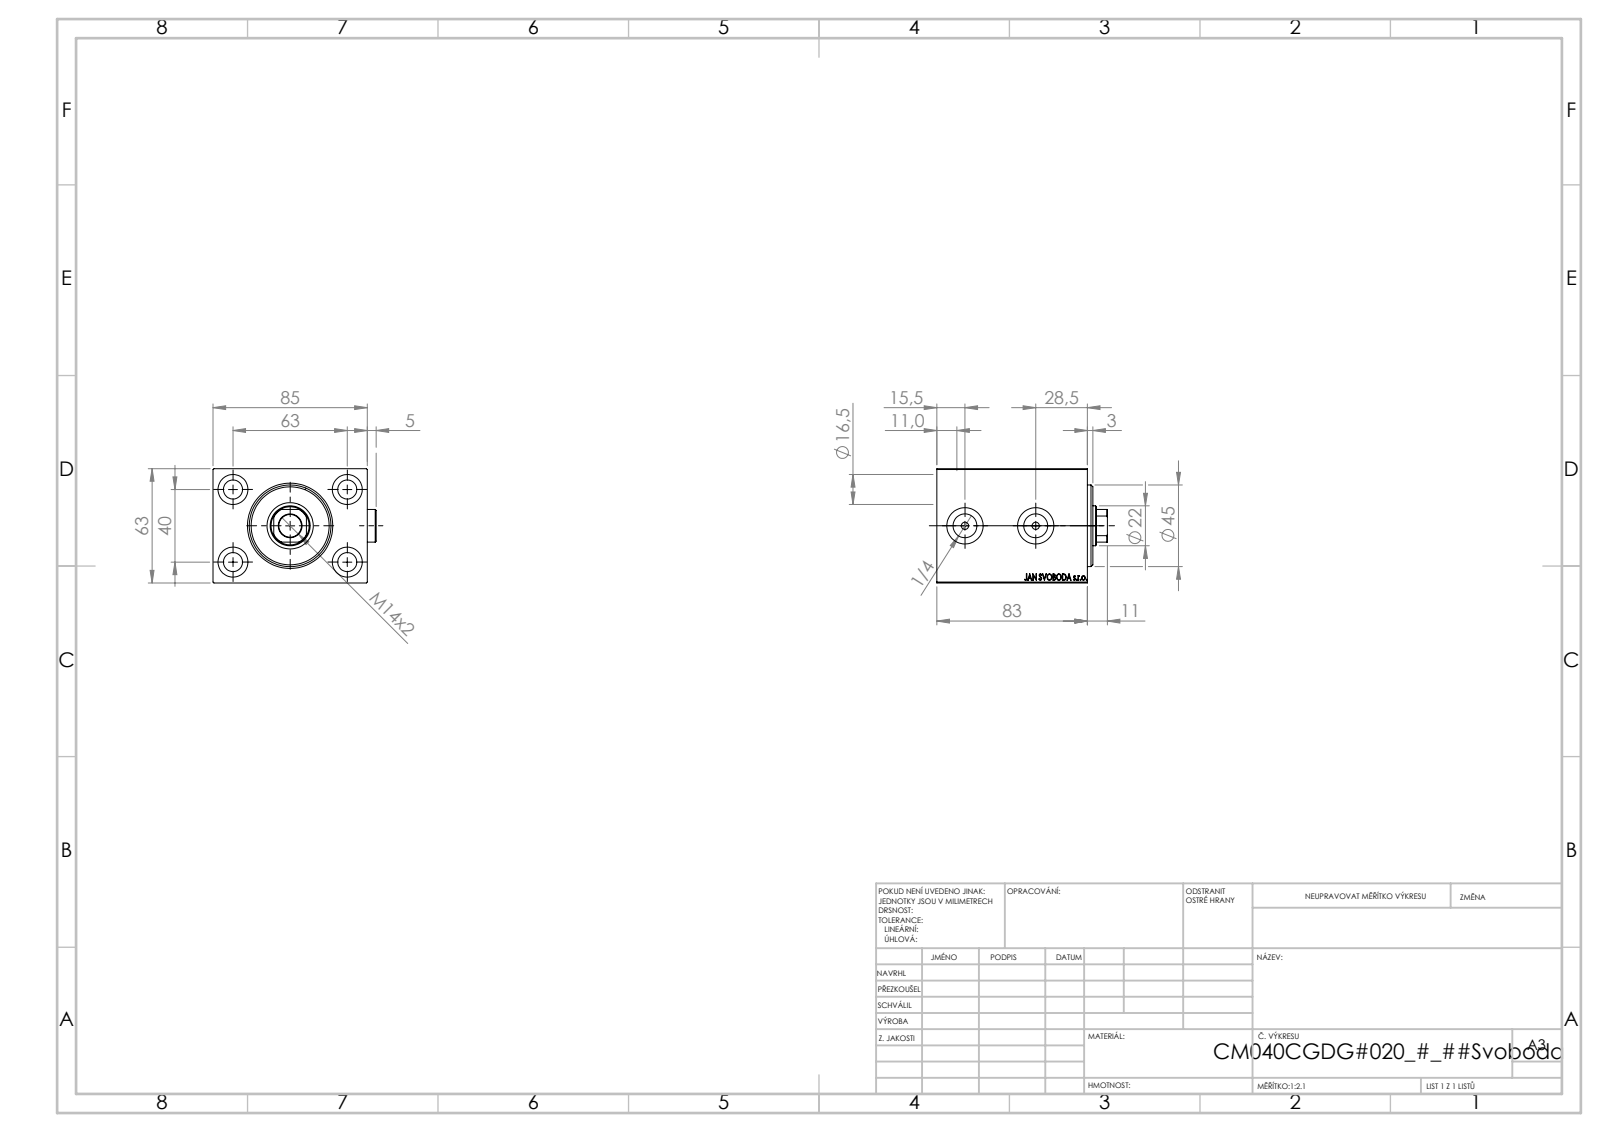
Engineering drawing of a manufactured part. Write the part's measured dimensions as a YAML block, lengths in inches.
part_name: "Zatka_OIL_PORT; V450CM_C_VCP; V450CM_VC_B; V450CM_C_Body"
step_written_by: "SolidWorks 2019 (CONFIG_CONTROL_DESIGN)"
units: inches
bodies: {solids: 5, faces: 914, planar: 442, cylindrical: 74, other: 398}
overall_size: [3.701, 3.539, 2.48]
volume: 24.06
surface_area: 115.4
round_holes:
  - {diameter: 0.413, count: 4}
  - {diameter: 0.65, count: 4}
  - {diameter: 0.157, count: 2}
  - {diameter: 0.518, count: 2}
  - {diameter: 0.787, count: 2}
  - {diameter: 0.492, count: 1}
  - {diameter: 0.866, count: 1}
  - {diameter: 1.004, count: 1}
  - {diameter: 1.575, count: 1}
  - {diameter: 1.654, count: 1}
  - {diameter: 1.772, count: 1}
round_bosses_or_shafts:
  - {diameter: 0.709, count: 2}
partial_cylinders:
  - {radius: 0.413, count: 1}
face_to_face_distances: [2.48, 3.346, 3.268, 1.26, 2.008, 2.835, 3.343, 0.433, 0.85, 1.157]
hole_center_spacings: [1.469, 1.575, 2.48, 2.938, 1.535]
